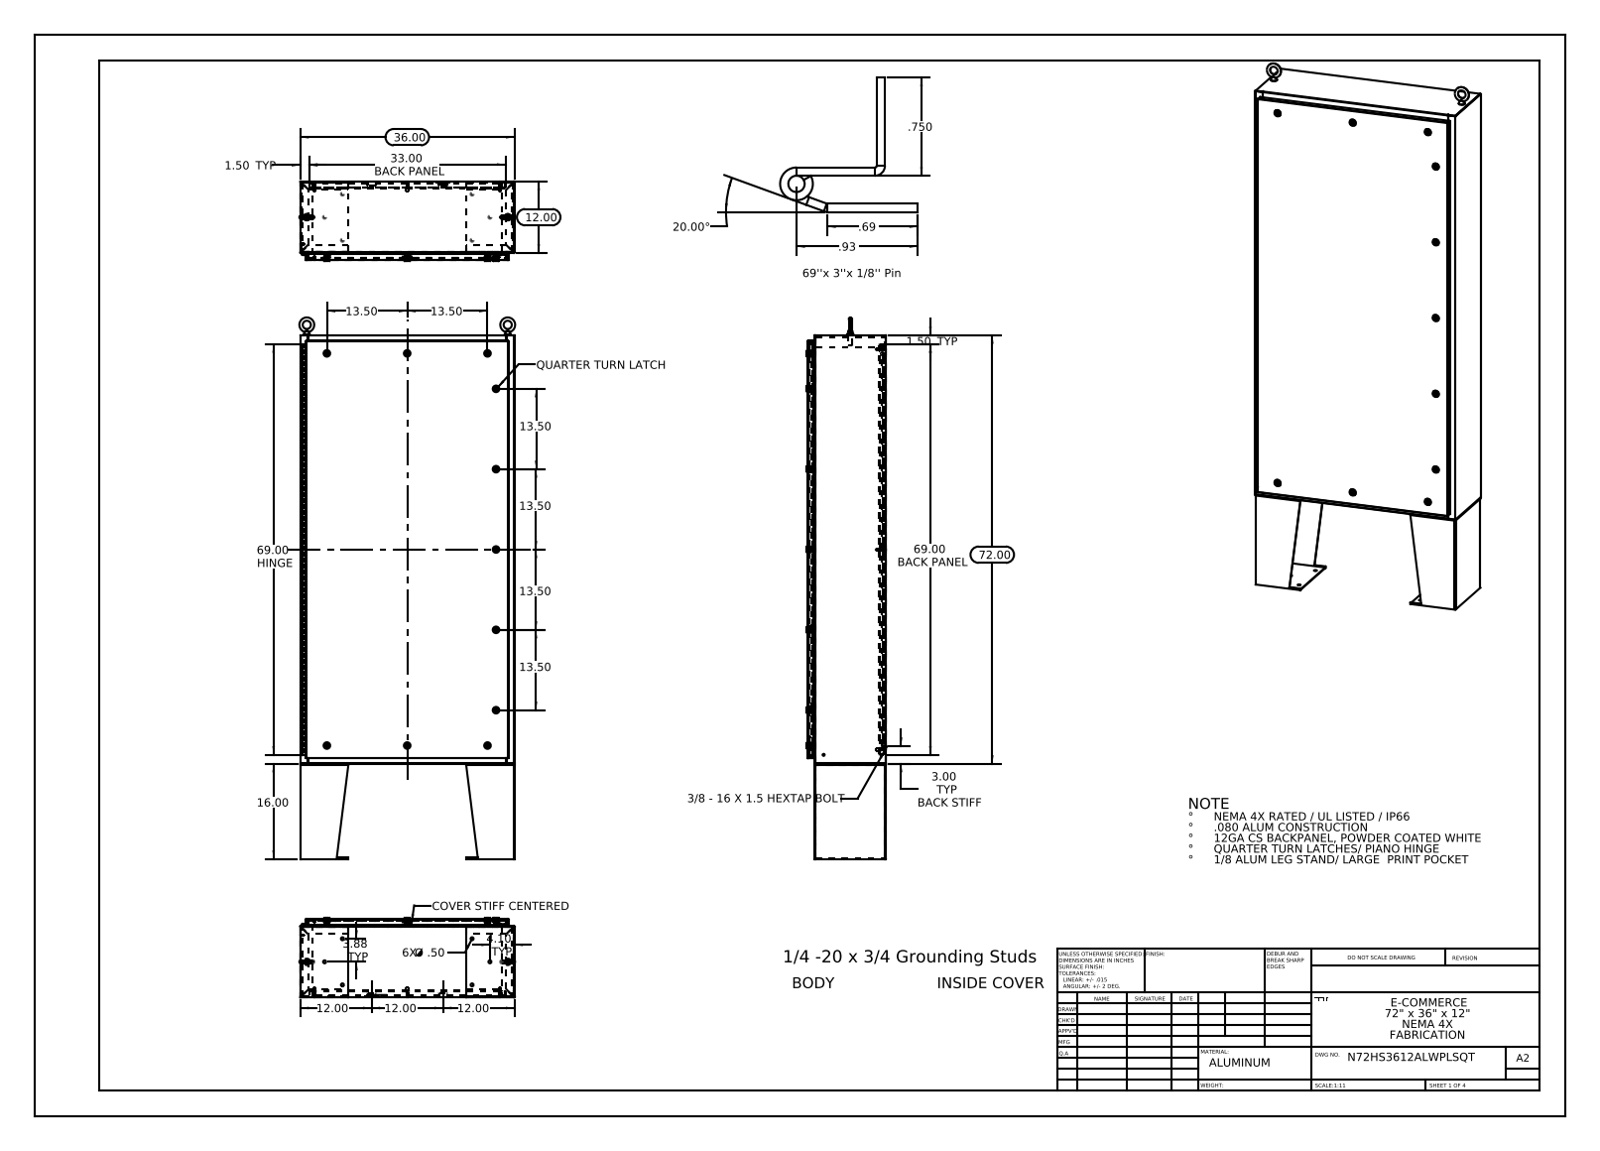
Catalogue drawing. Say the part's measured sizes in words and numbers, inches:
The part is named "N72HS3612SSWPLSQT SD-LSK-ASSY; N72HS3612SSWPLSQT Backpanel; N72HS3612SSWPLSQT Mounting Studs; N72HS3612SSWPLSQT Hinge Cover Side (+8 more)". Its 3-D file was written by "SolidWorks 2013 (CONFIG_CONTROL_DESIGN)". It is 36 solids with 2637 faces: 1327 planar, 1114 cylindrical and 196 other. Overall it measures 91 by 36.271 by 13.201 inches. Its volume is 1 059 cubic inches and its surface area 25 612 square inches. Round holes: 14 of diameter 0.5, 8 of diameter 0.25, 4 of diameter 0.75, 1 of diameter 0.125, 1 of diameter 0.125. Round bosses or shafts: 10 of diameter 0.625, 8 of diameter 0.375, 8 of diameter 0.33, 8 of diameter 0.157, 8 of diameter 0.14, 2 of diameter 0.315, 2 of diameter 0.236, 1 of diameter 0.25. Partial cylindrical surfaces (rounded edges, fillets, slot ends): 36 of radius 0.013, 30 of radius 0.088, 8 of radius 0.039, 8 of radius 0.143, 6 of radius 0.019, 6 of radius 0.442, 4 of radius 0.117, 4 of radius 0.125. The main face-to-face distances are 0.075, 13.126, 0.104, 13.051, 1.075, 13.201, 12.126, 1, 12.051, 1.179. The hole center spacings are 2.225, 7.137, 25.094, 33.625, 37.078, 45.904, 69.041, 17.33.
